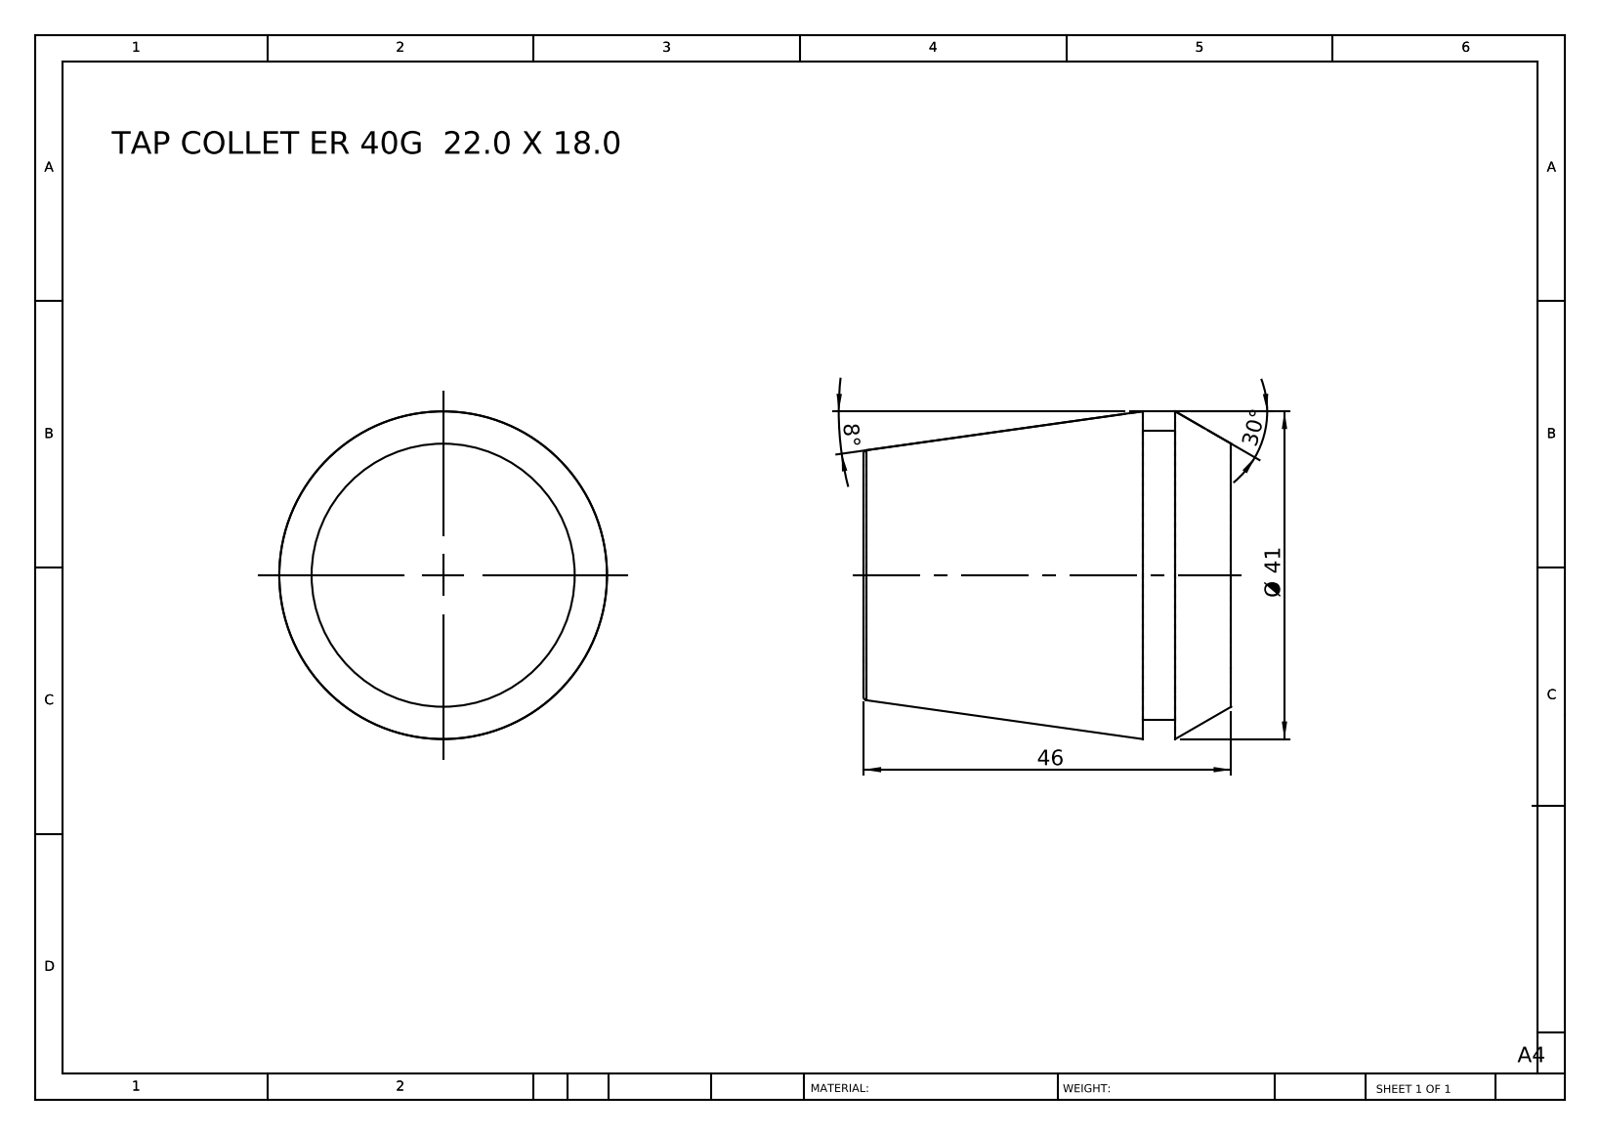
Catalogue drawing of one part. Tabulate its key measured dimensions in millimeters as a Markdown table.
| quantity | value |
| --- | --- |
| part name | TAP COLLET ER 40G 22.0 X 18.0 |
| STEP written by | SolidWorks 2014 (CONFIG_CONTROL_DESIGN) |
| units | millimeters |
| bodies | 1 solid, 12 faces (4 planar, 2 cylindrical, 6 other) |
| overall size | 46 × 41 × 41 |
| volume | 47 690 mm³ |
| surface area | 7 586 mm² |
| round bosses / shafts (diameter × count) | 36.2 × 1 |
| main face-to-face distances | 46, 11.1, 34.9, 7, 4.1, 39 |
